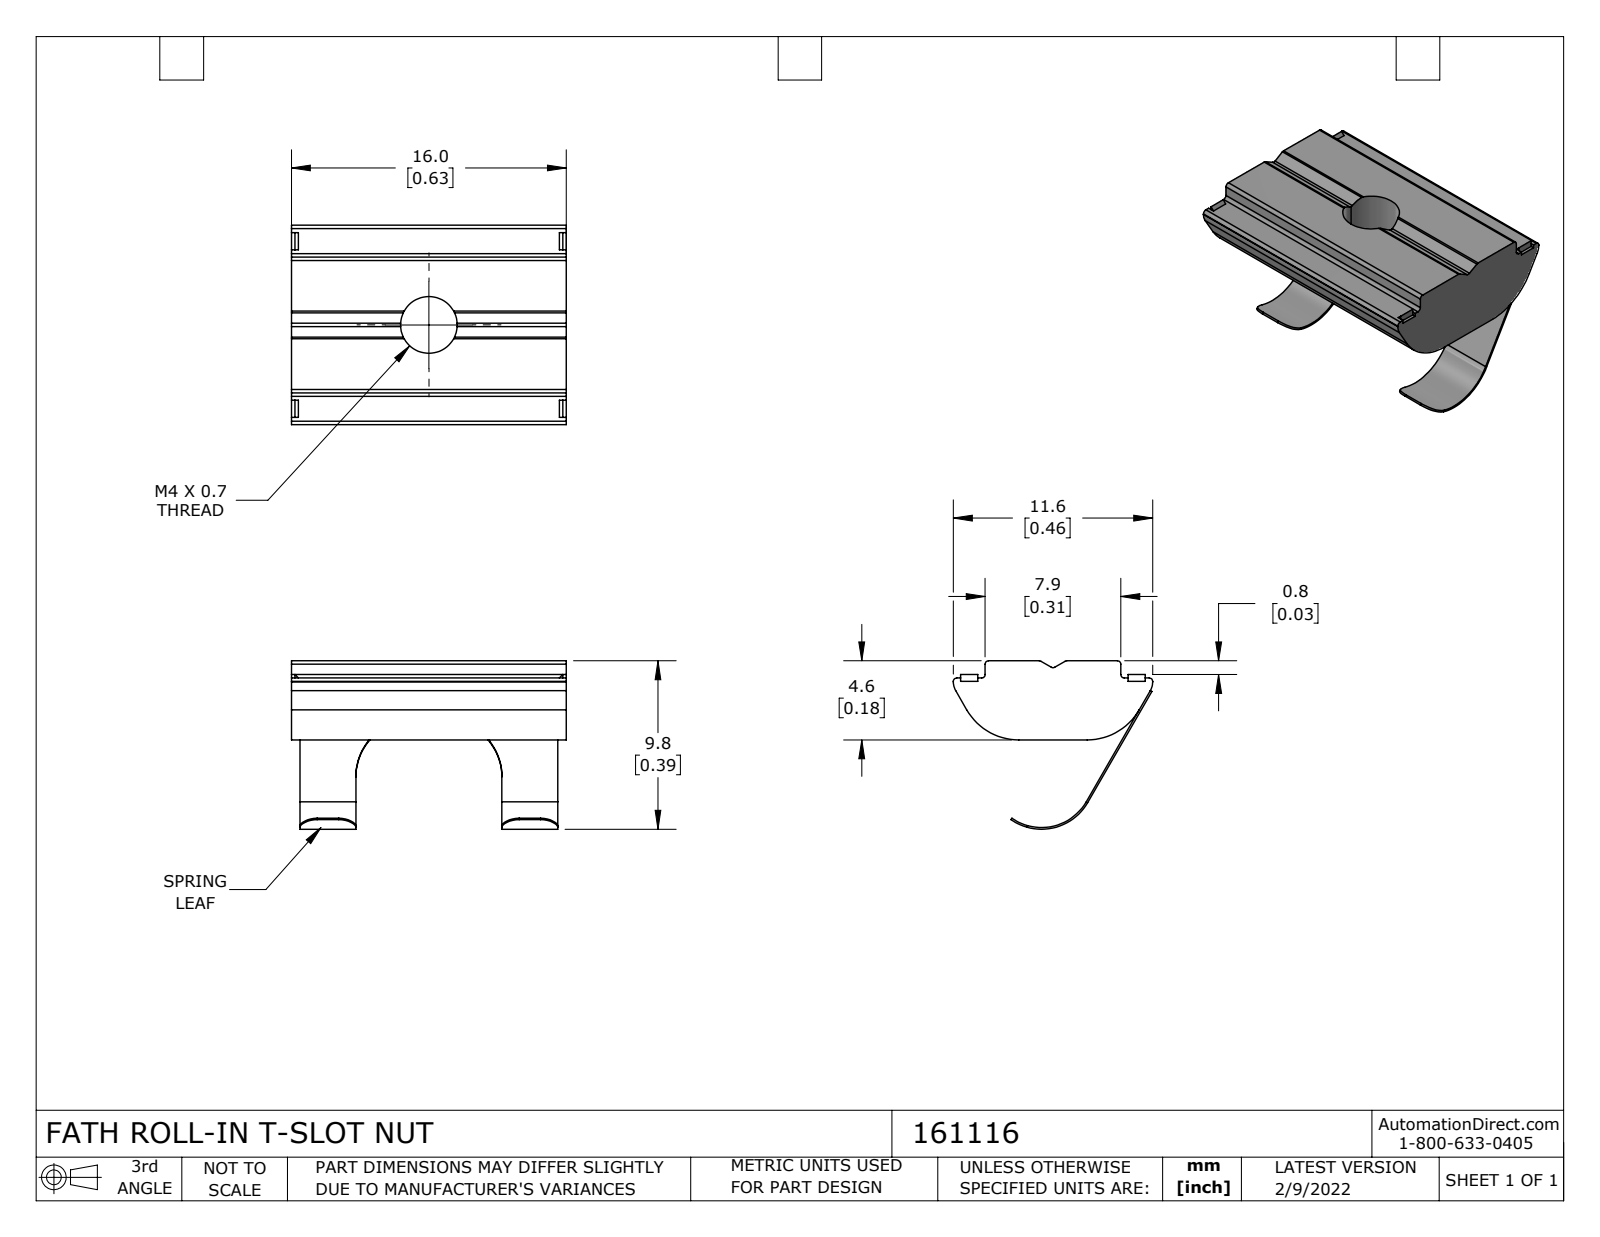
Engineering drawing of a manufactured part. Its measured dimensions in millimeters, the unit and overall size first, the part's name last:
Units: millimetres
Overall size (bounding box): 16 × 11.6 × 9.8
Round holes (diameter × count): ⌀3.3 ×1
Partial cylindrical surfaces — rounded edges, fillets, slot ends (radius × count): R0.2 ×9, R1 ×6, R3.5 ×2, R3 ×1, R3.1 ×1, R4.25 ×1
Main face-to-face distances: 4.6, 1, 3.6, 16, 7.9, 0.5, 15.5, 15.8, 15.3, 1.71
Volume: 651 mm³ · Surface area: 745 mm²
Bodies: 1 solid, 83 faces (55 planar, 28 cylindrical, 0 other)
Part name (STEP PRODUCT): 161116
STEP written by: SolidWorks 2021 (CONFIG_CONTROL_DESIGN)
